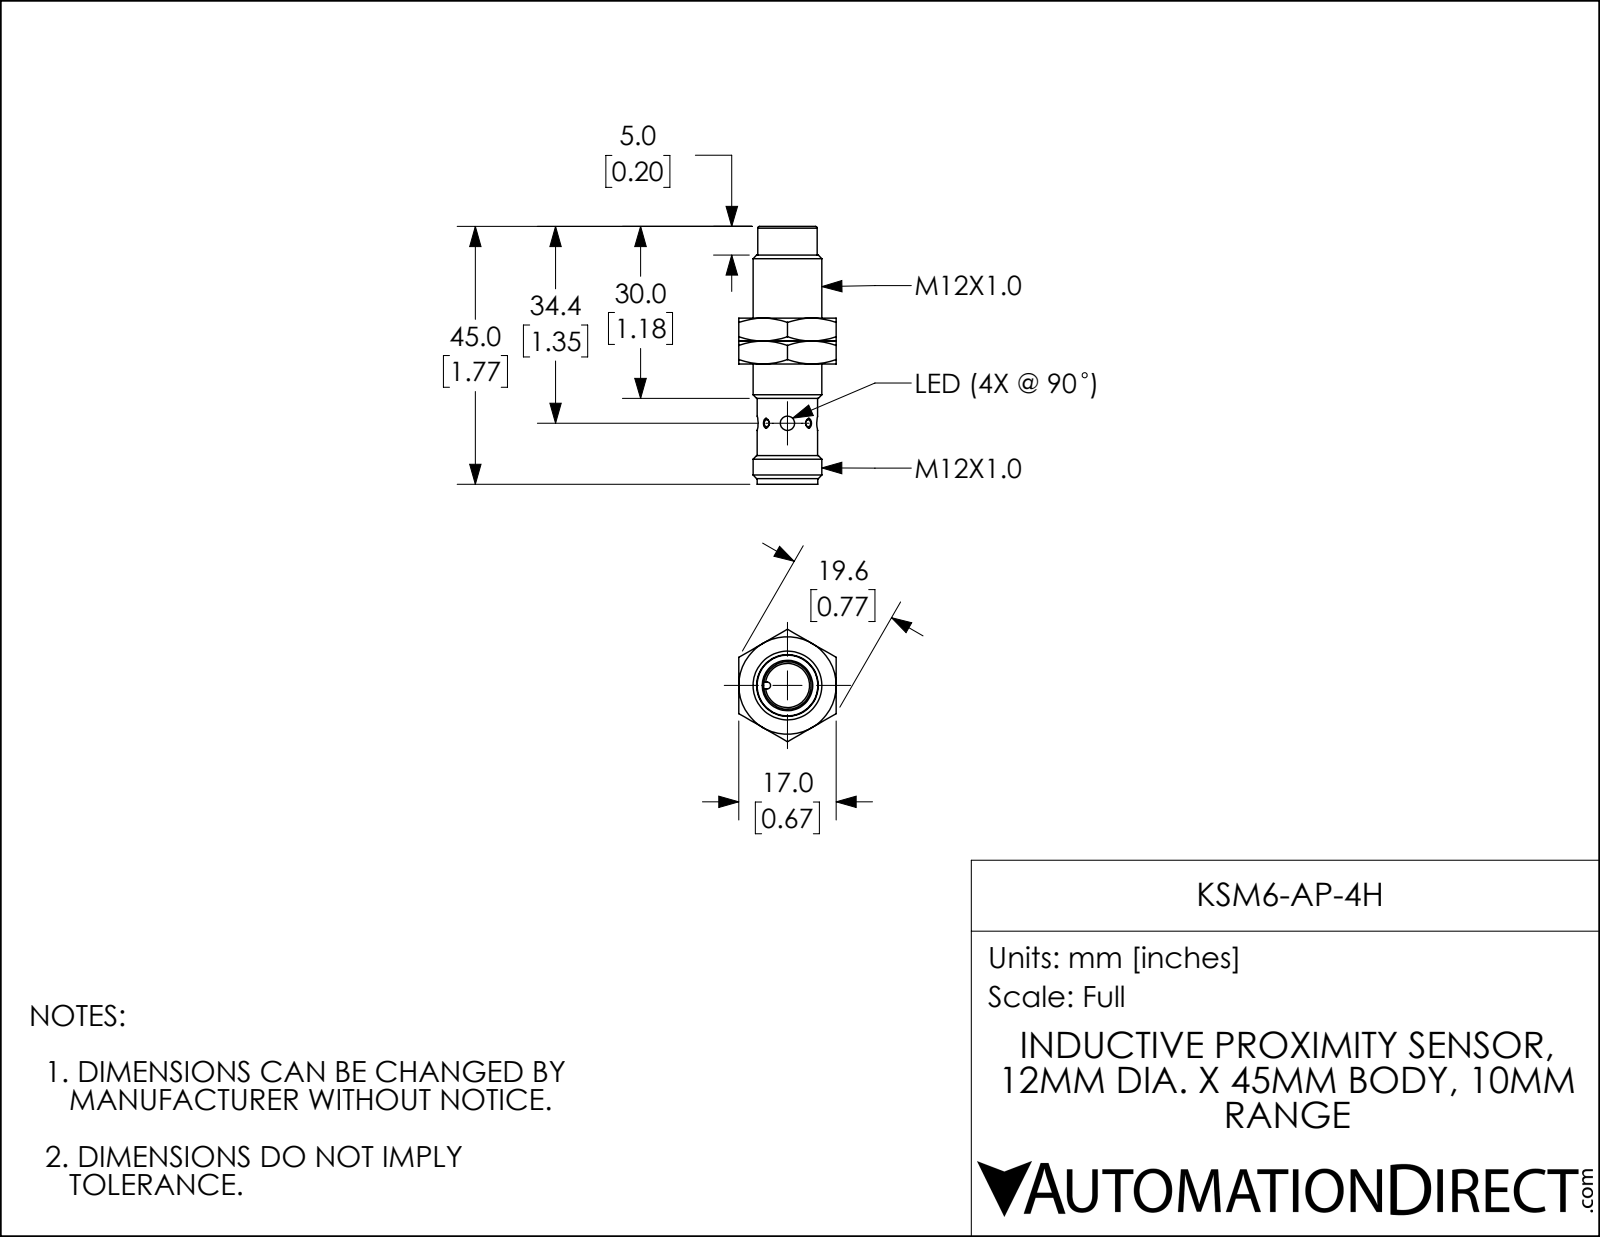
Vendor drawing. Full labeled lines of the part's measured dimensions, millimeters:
Part name (STEP PRODUCT): KSM6-AP-4H
STEP written by: SolidWorks 2017 (AUTOMOTIVE_DESIGN)
Units: millimetres
Bodies: 3 solids, 86 faces (26 planar, 13 cylindrical, 47 other)
Overall size (bounding box): 45 × 19.6 × 17
Volume: 5 360 mm³ · Surface area: 3 381 mm²
Round holes (diameter × count): ⌀2.5 ×2, ⌀8.3 ×1, ⌀10.9 ×1
Round bosses / shafts (diameter × count): ⌀12 ×1, ⌀10.6 ×1, ⌀10.5 ×1, ⌀10.4 ×1
Partial cylindrical surfaces — rounded edges, fillets, slot ends (radius × count): R0.6 ×1
Main face-to-face distances: 4, 17, 8, 20, 24, 16, 12.1, 16.1, 20.1, 36.1
